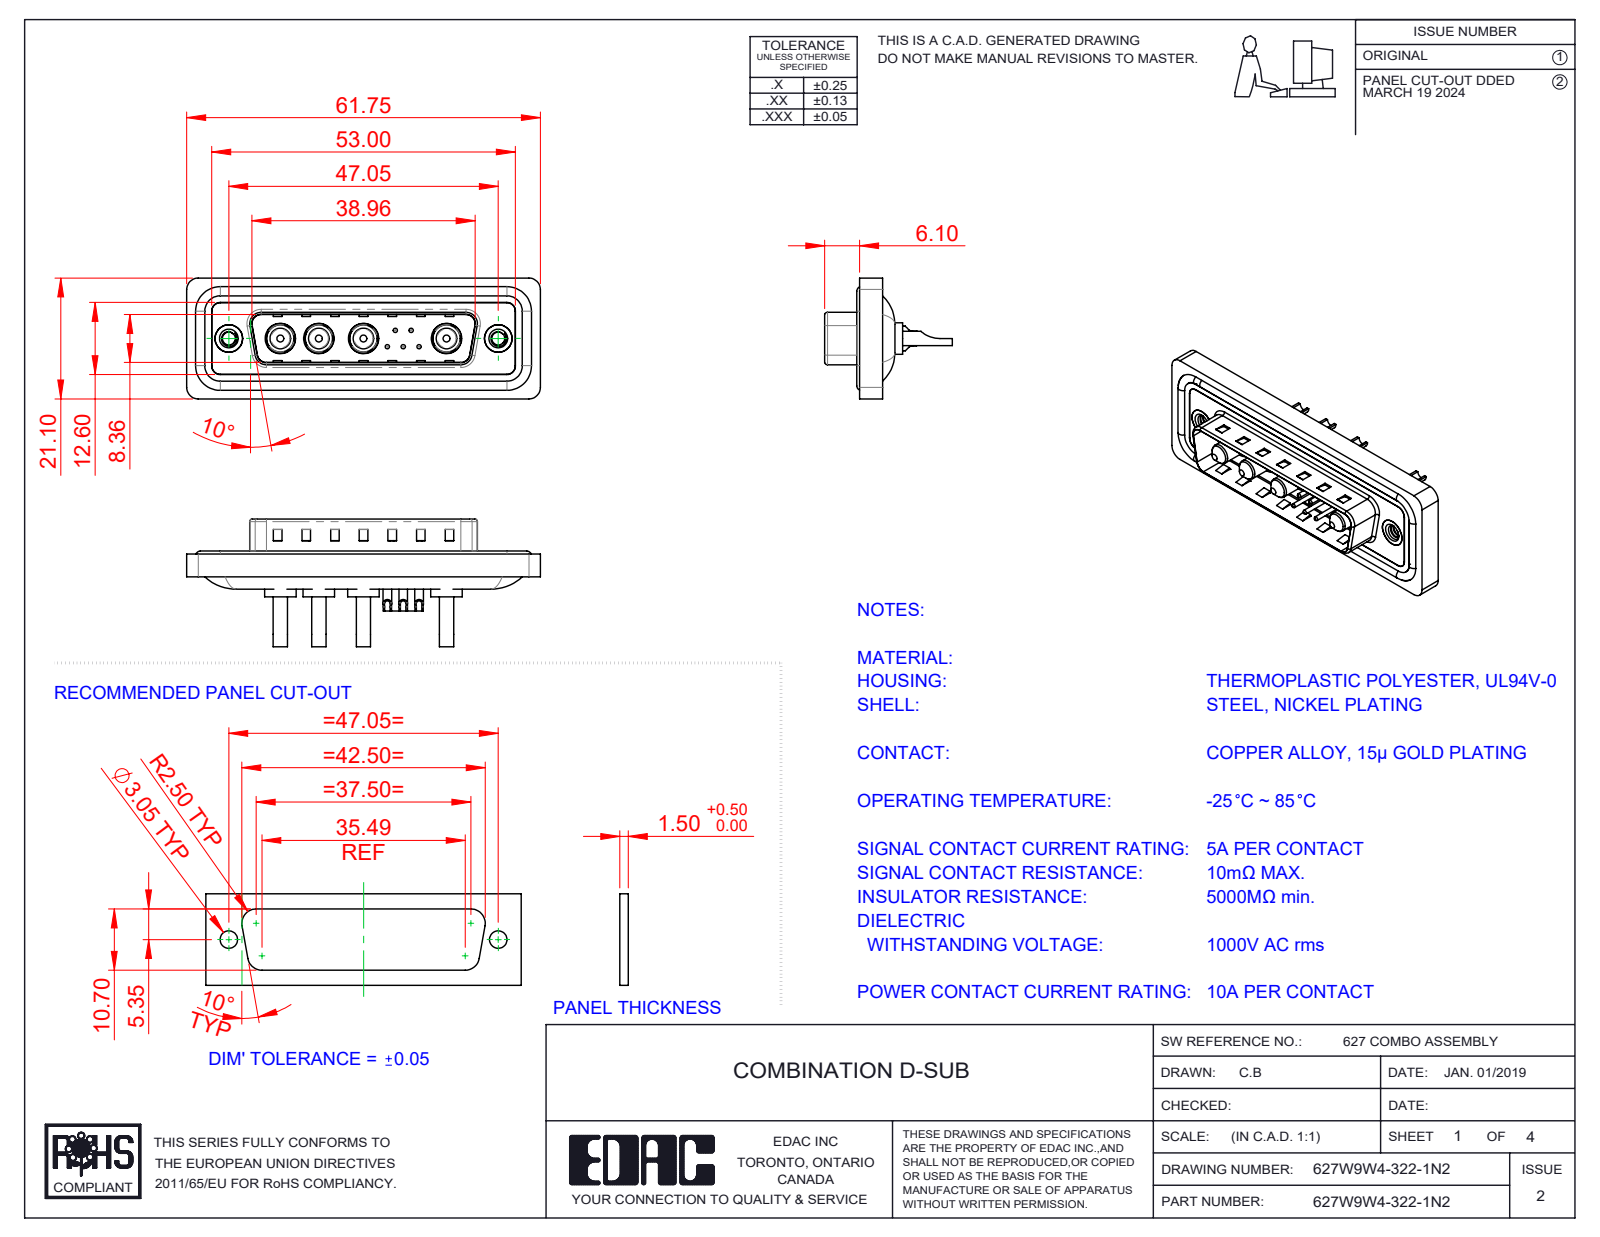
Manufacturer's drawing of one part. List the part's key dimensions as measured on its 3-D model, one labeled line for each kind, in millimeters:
Part name (STEP PRODUCT): 627Combo Threaded Rivet_2; 627Combo Contact Row 2_22; 627Combo Contact Row 1_22; 627Combo Shell Front_25 Contacts (+5 more)
STEP written by: SolidWorks 2023 (CONFIG_CONTROL_DESIGN)
Units: millimetres
Bodies: 20 solids, 848 faces (302 planar, 356 cylindrical, 190 other)
Overall size (bounding box): 61.75 × 22.3 × 21.1
Volume: 7 401 mm³ · Surface area: 12 066 mm²
Round holes (diameter × count): ⌀0.75 ×5, ⌀1 ×5, ⌀1.6 ×5, ⌀2 ×5, ⌀1.7 ×4, ⌀4.85 ×4, ⌀5.3 ×4, ⌀2.26 ×2, ⌀4 ×2, ⌀4.8 ×2, ⌀5 ×2
Round bosses / shafts (diameter × count): ⌀1.5 ×5, ⌀5.5 ×4, ⌀5.2 ×4, ⌀4.75 ×4, ⌀3.75 ×4, ⌀3.6 ×4, ⌀2.5 ×4, ⌀1.6 ×4
Partial cylindrical surfaces — rounded edges, fillets, slot ends (radius × count): R1.5 ×22, R2 ×18, R0.5 ×8, R1.6 ×8, R1 ×6, R0.25 ×4, R0.6 ×4, R0.65 ×4
Main face-to-face distances: 0.4, 1.5, 1.1, 0.5, 1.6, 3.1, 2.9, 0.82, 9.58, 5.65
Hole centre spacings: 3.16, 2.77, 5.04, 14.51, 2.78, 4.4, 4.41, 5
